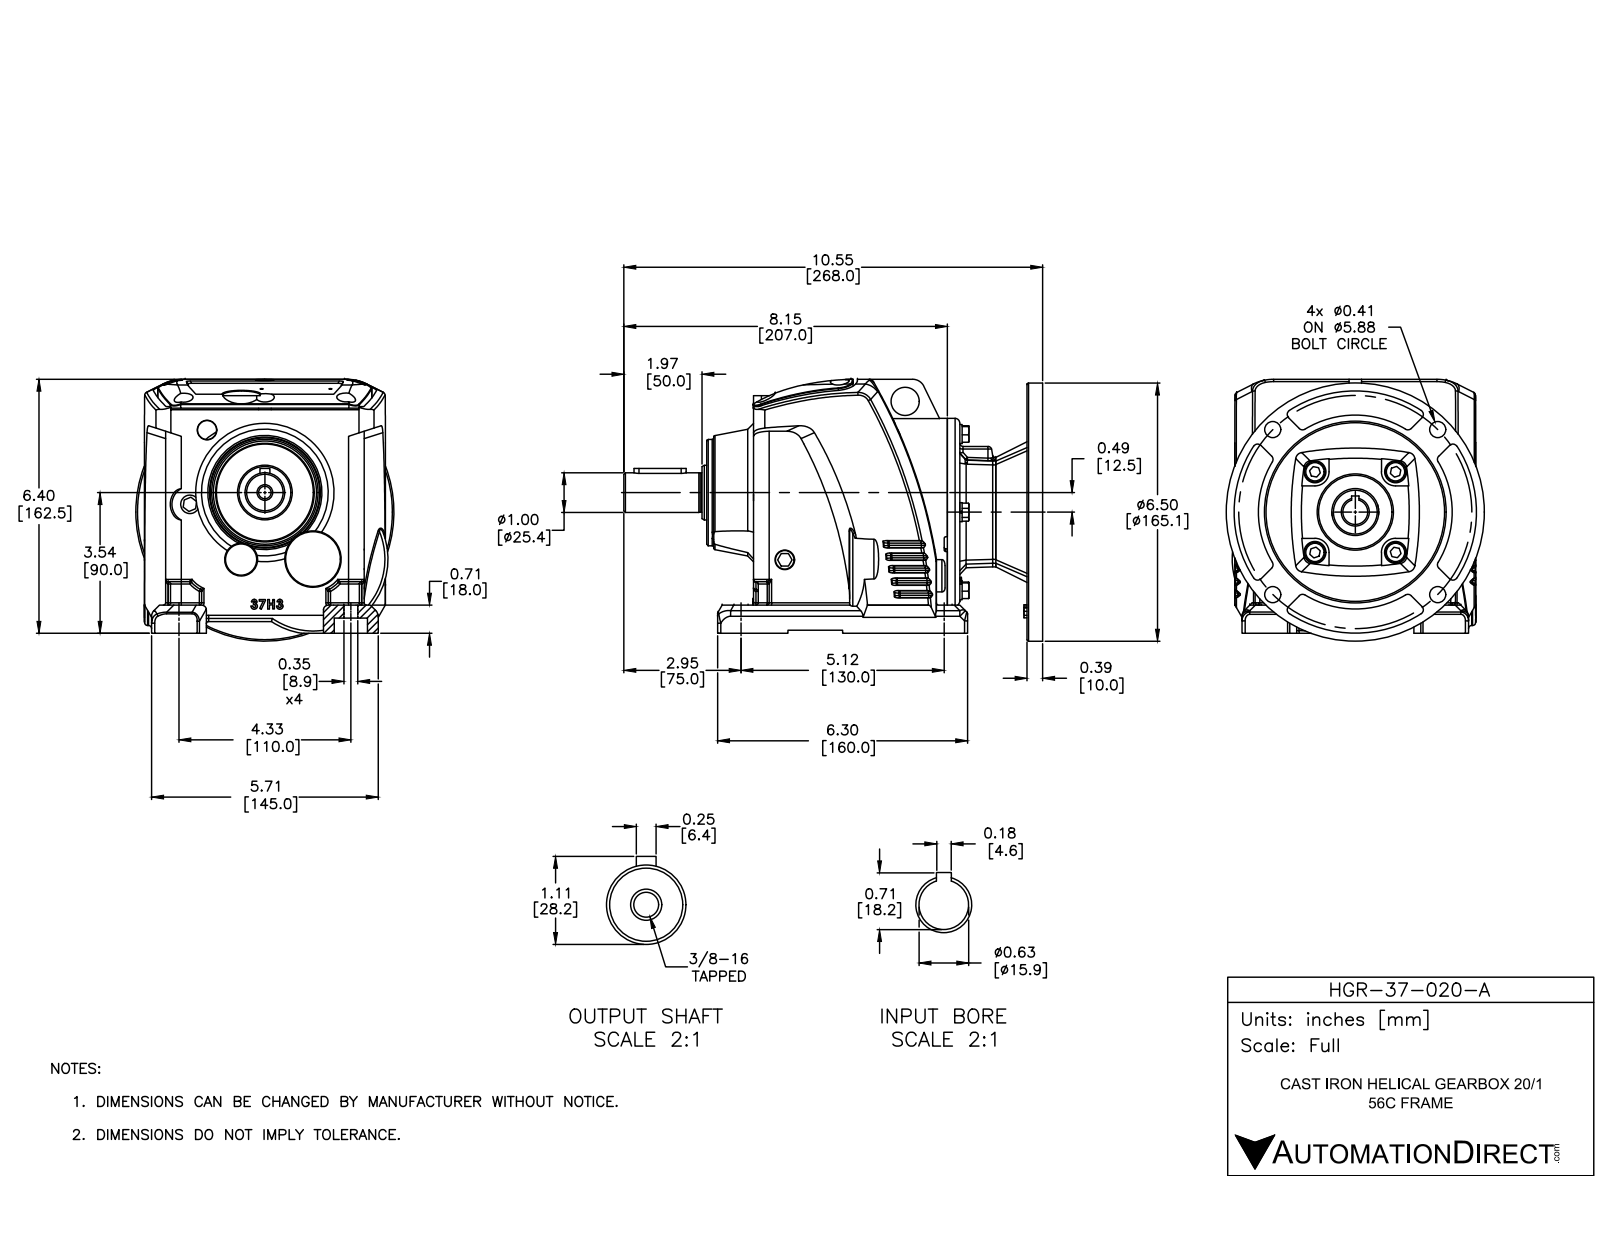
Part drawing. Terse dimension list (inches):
name: HGR-37-020-A
written by: SolidWorks 2015 (AUTOMOTIVE_DESIGN)
unit: in
bodies: 4 solids, 1036 faces (343 planar, 277 cylindrical, 416 other)
size: 10.551 × 6.596 × 6.5
volume: 169.7 in³; area: 383.8 in²
holes: 6× ⌀0.472, 4× ⌀0.406, 4× ⌀0.55, 3× ⌀0.276, 2× ⌀0.079, 2× ⌀0.354, 2× ⌀0.394, 1× ⌀0.313, 1× ⌀0.625, 1× ⌀0.709, 1× ⌀0.945, 1× ⌀1.181
bosses: 4× ⌀0.512, 4× ⌀0.48, 4× ⌀0.315, 2× ⌀1.378, 2× ⌀0.472, 1× ⌀6.5, 1× ⌀4.724, 1× ⌀2.677
rounds: 43× R0.059, 21× R0.118, 18× R0.079, 8× R0.197, 6× R0.354, 6× R0.394, 5× R0.315, 4× R0.276
face distances: 7.126, 0.236, 0.276, 0.394, 6.89, 1.102, 4.331, 0.157, 2.087, 0.079
hole spacings: 3.27, 1.437, 1.5, 2.032, 2.937, 4.154, 4.374, 1.143
